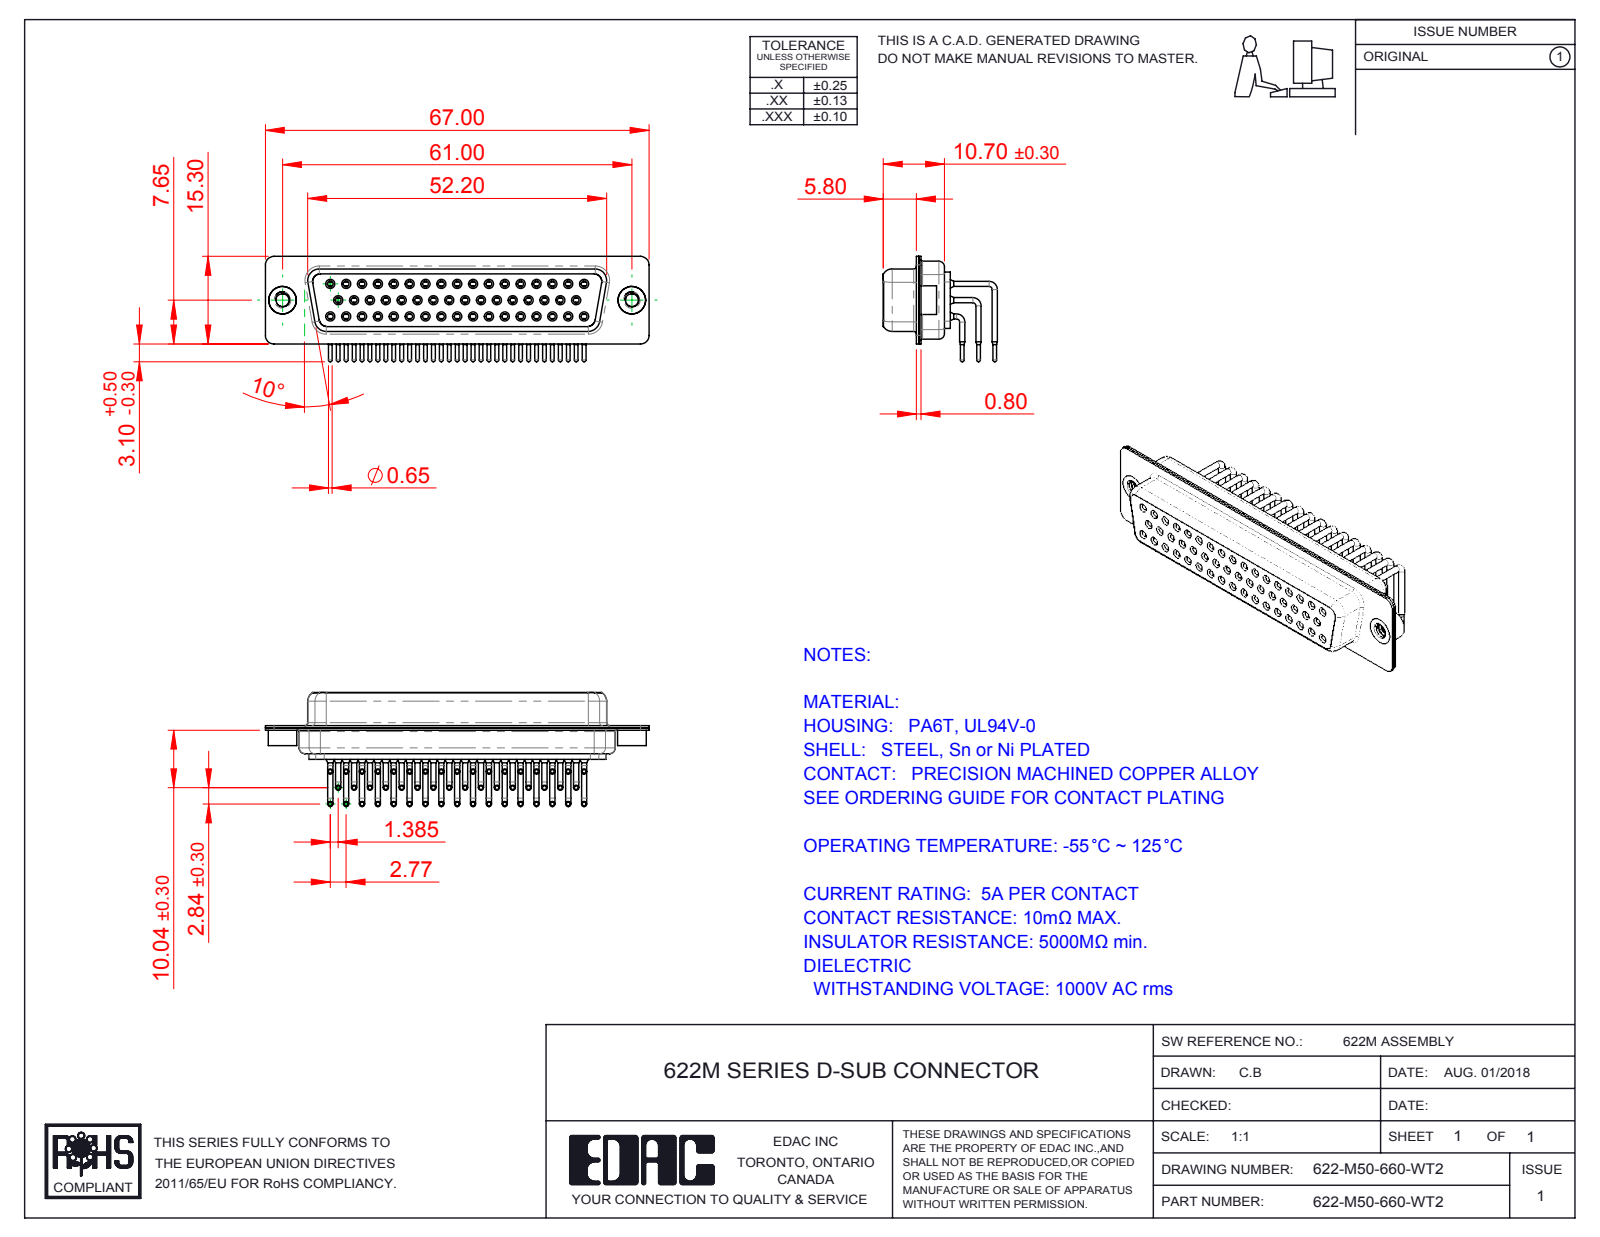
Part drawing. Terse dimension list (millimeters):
name: 622-M50-660-WT2; 622M 4-40 Threaded Rivet; 622M Contact Row 2_50 Contacts; 622M Contact Row 1_50 Contacts (+4 more)
written by: SolidWorks 2016 (CONFIG_CONTROL_DESIGN)
unit: mm
bodies: 55 solids, 2929 faces (817 planar, 1287 cylindrical, 825 other)
size: 67 × 19.93 × 18.4
volume: 6 933 mm³; area: 16 132 mm²
holes: 50× ⌀1, 50× ⌀1.1, 50× ⌀1.7, 50× ⌀1.8, 50× ⌀2, 2× ⌀2.26, 2× ⌀4, 2× ⌀4.8
bosses: 100× ⌀0.9, 50× ⌀1.6, 50× ⌀1.5, 50× ⌀0.65, 2× ⌀5, 2× ⌀4.9
rounds: 16× R1.5, 12× R2, 8× R1.35, 8× R1.6, 4× R0.25, 4× R0.5, 4× R0.6, 4× R0.65
face distances: 0.4, 1.35, 11.85, 0.85, 2.2, 5.5, 12.25, 5.9, 10.5, 0.8
hole spacings: 2.77, 3.16, 5.54, 8.31, 11.08, 13.85, 16.62, 19.39
